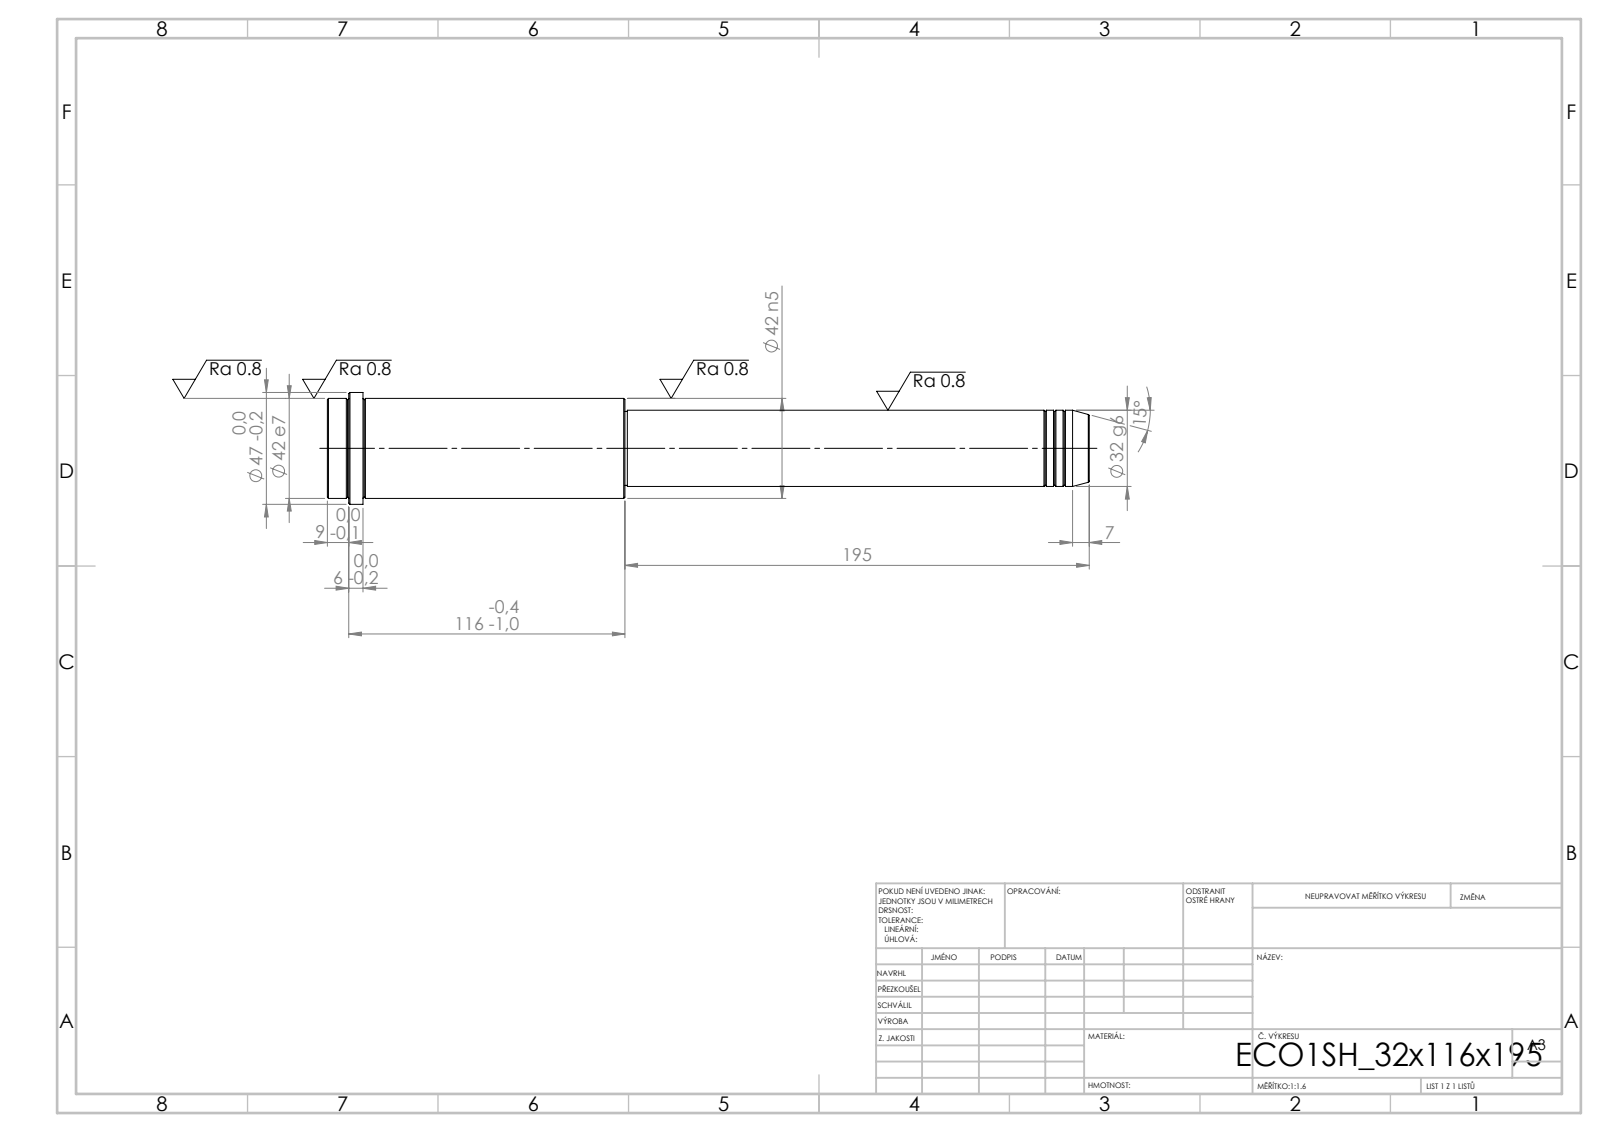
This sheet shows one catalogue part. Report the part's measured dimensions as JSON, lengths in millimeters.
{"step_written_by": "SolidWorks 2019 (CONFIG_CONTROL_DESIGN)", "units": "millimeters", "bodies": {"solids": 1, "faces": 52, "planar": 6, "cylindrical": 16, "other": 30}, "overall_size": [320, 47, 47], "volume_mm3": 331149, "surface_area_mm2": 39737, "round_bosses_or_shafts": [[47, 1], [42, 1], [32, 1], [31, 1]], "face_to_face_distances": [320, 195, 125, 305, 110, 15, 311, 116, 6, 9]}
